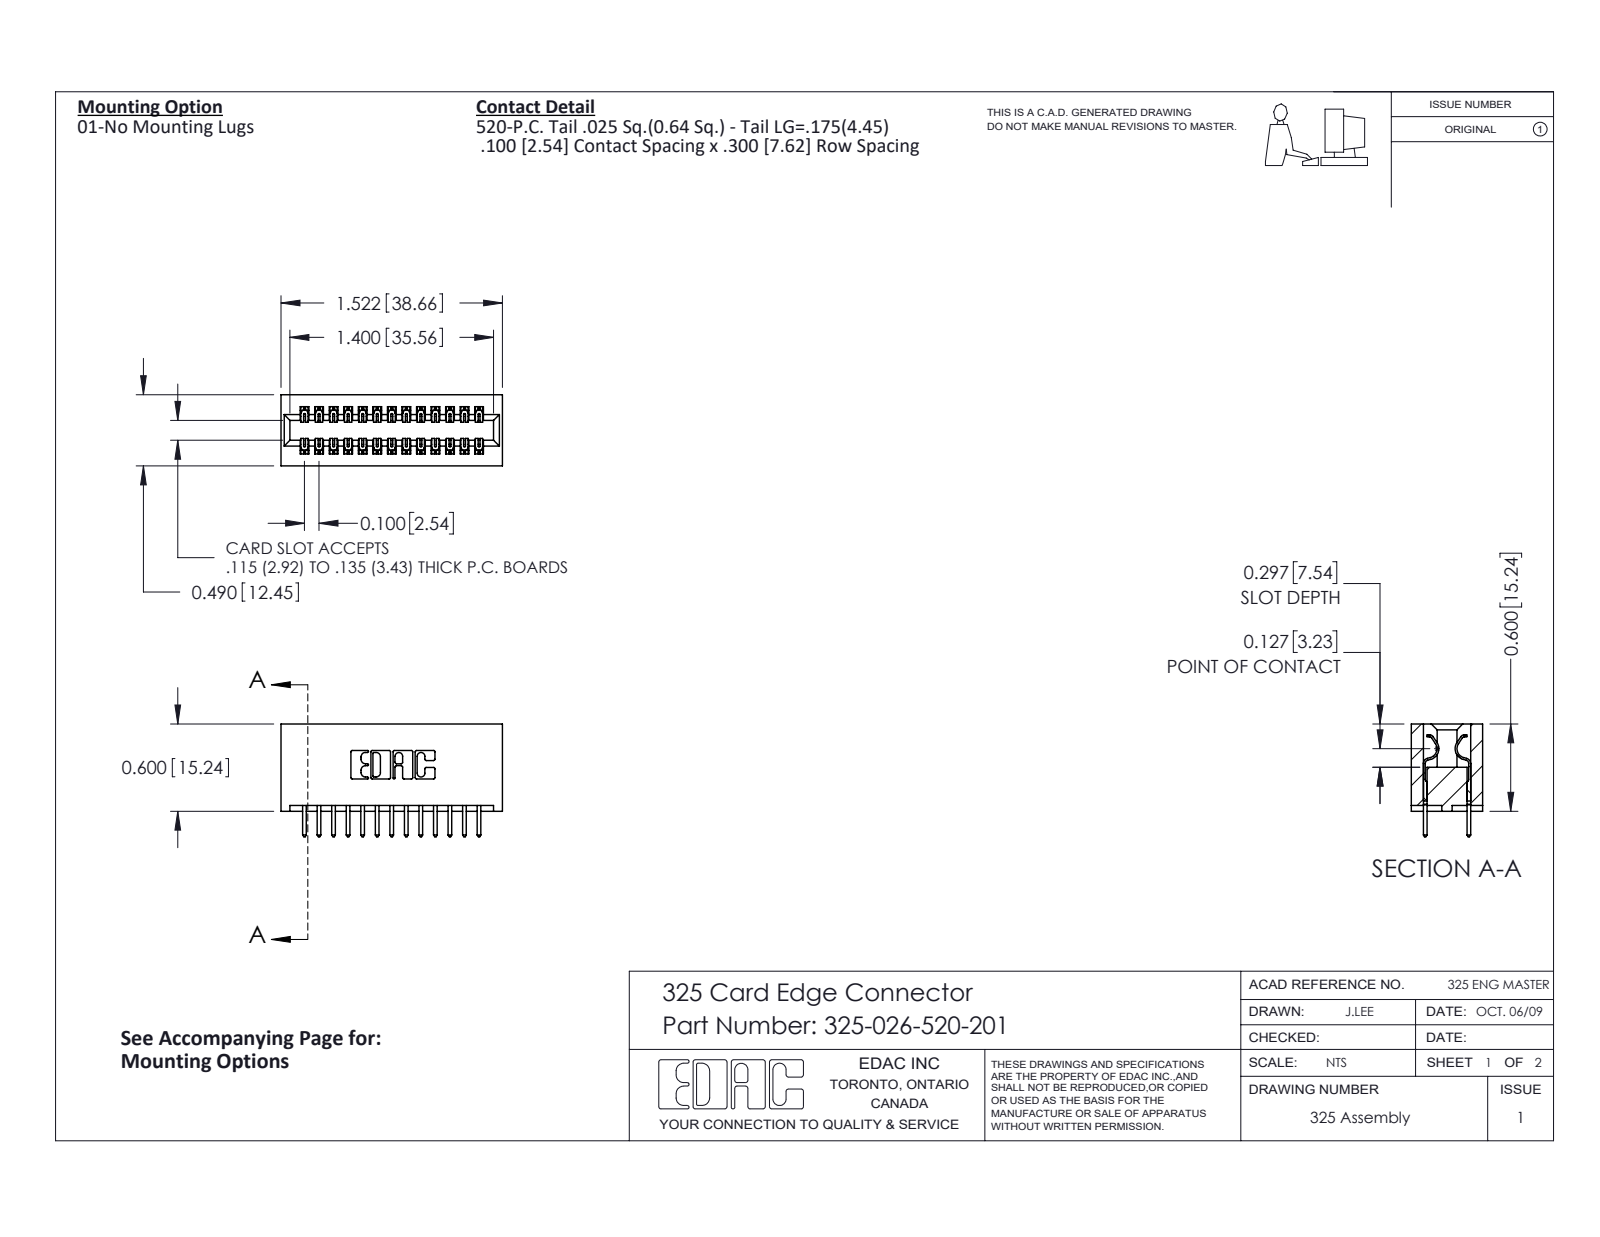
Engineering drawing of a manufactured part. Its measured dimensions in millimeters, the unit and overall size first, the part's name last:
Units: millimetres
Overall size (bounding box): 38.7 × 19.7 × 12.4
Partial cylindrical surfaces — rounded edges, fillets, slot ends (radius × count): R0.2 ×39, R0.3 ×26, R0.3 ×22, R0.2 ×6, R0.8 ×6, R0.7 ×3, R0.4 ×2, R0.6 ×2
Main face-to-face distances: 2.1, 10.3, 7.6, 2.5, 12.4, 2.7, 9.7, 0.6, 5.1, 15.2
Volume: 5 330 mm³ · Surface area: 6 375 mm²
Bodies: 27 solids, 1458 faces (1002 planar, 456 cylindrical, 0 other)
Part name (STEP PRODUCT): 325-026-520-201; 325 Part_Lugless; 325-292-001_325-293-120
STEP written by: SolidWorks 2016 (CONFIG_CONTROL_DESIGN)
